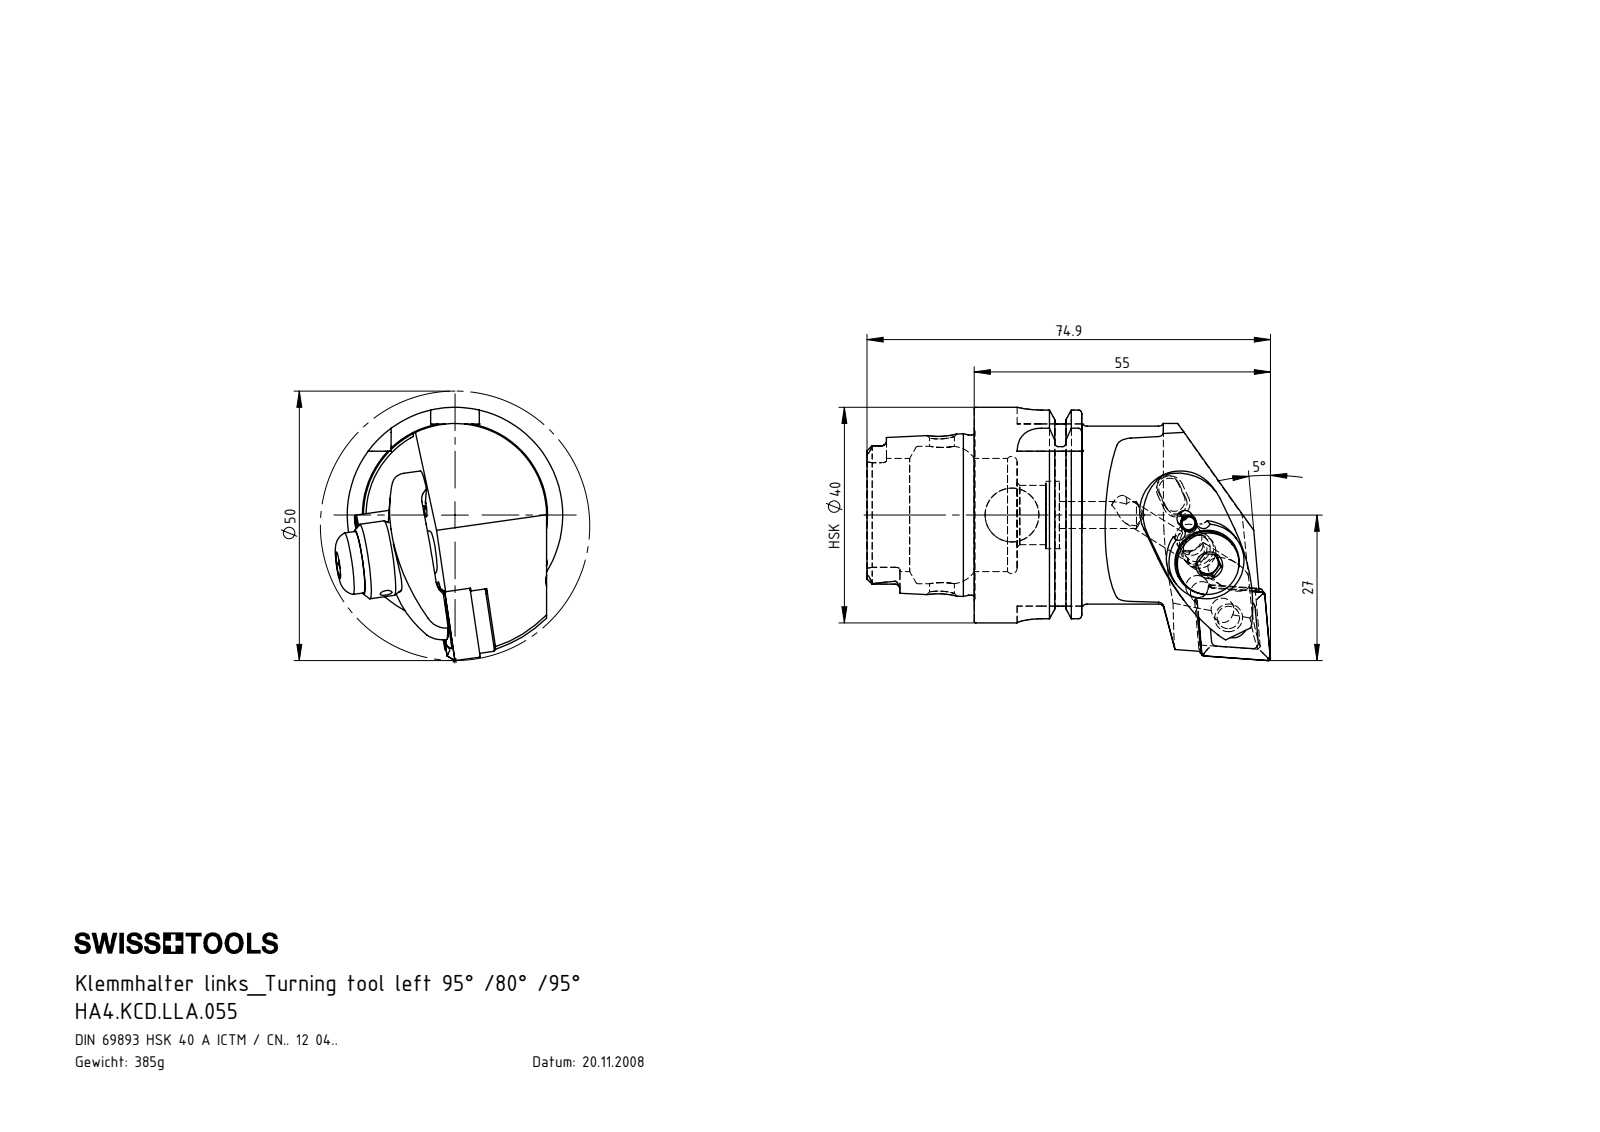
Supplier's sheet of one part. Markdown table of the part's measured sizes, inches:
| quantity | value |
| --- | --- |
| part name | HA4-KCD.LLA.055_B_Fertigbearbeitung; WCD-ER2.101.003_A; WCC-ER2.001.010_A; CNMG120404 (+7 more) |
| STEP written by | SolidWorks 2017 (CONFIG_CONTROL_DESIGN) |
| units | inches |
| bodies | 11 solids, 480 faces (129 planar, 158 cylindrical, 193 other) |
| overall size | 2.949 × 1.85 × 1.662 |
| volume | 2.945 in³ |
| surface area | 29.13 in² |
| round holes (diameter × count) | 0.079 × 3, 0.165 × 3, 0.197 × 3, 0.276 × 2, 0.094 × 1, 0.118 × 1, 0.157 × 1, 0.181 × 1, 0.203 × 1, 0.244 × 1, 0.252 × 1, 0.335 × 1 |
| round bosses / shafts (diameter × count) | 0.197 × 2, 0.118 × 2, 1.575 × 1, 1.368 × 1, 1.299 × 1, 1.17 × 1, 0.551 × 1, 0.453 × 1 |
| partial cylindrical surfaces (radius × count) | 0.015 × 6, 0.035 × 6, 0.016 × 4, 0.039 × 4, 0.177 × 4, 0.027 × 3, 0.027 × 3, 0.059 × 3 |
| main face-to-face distances | 0.313, 0.177, 0.227, 0.05, 0.472, 0.785, 0.783, 1.096, 1.569, 0.5 |
| hole center spacings | 0.315, 0.588, 0.903, 0.304, 0.591, 0.608, 0.906, 0.296 |
